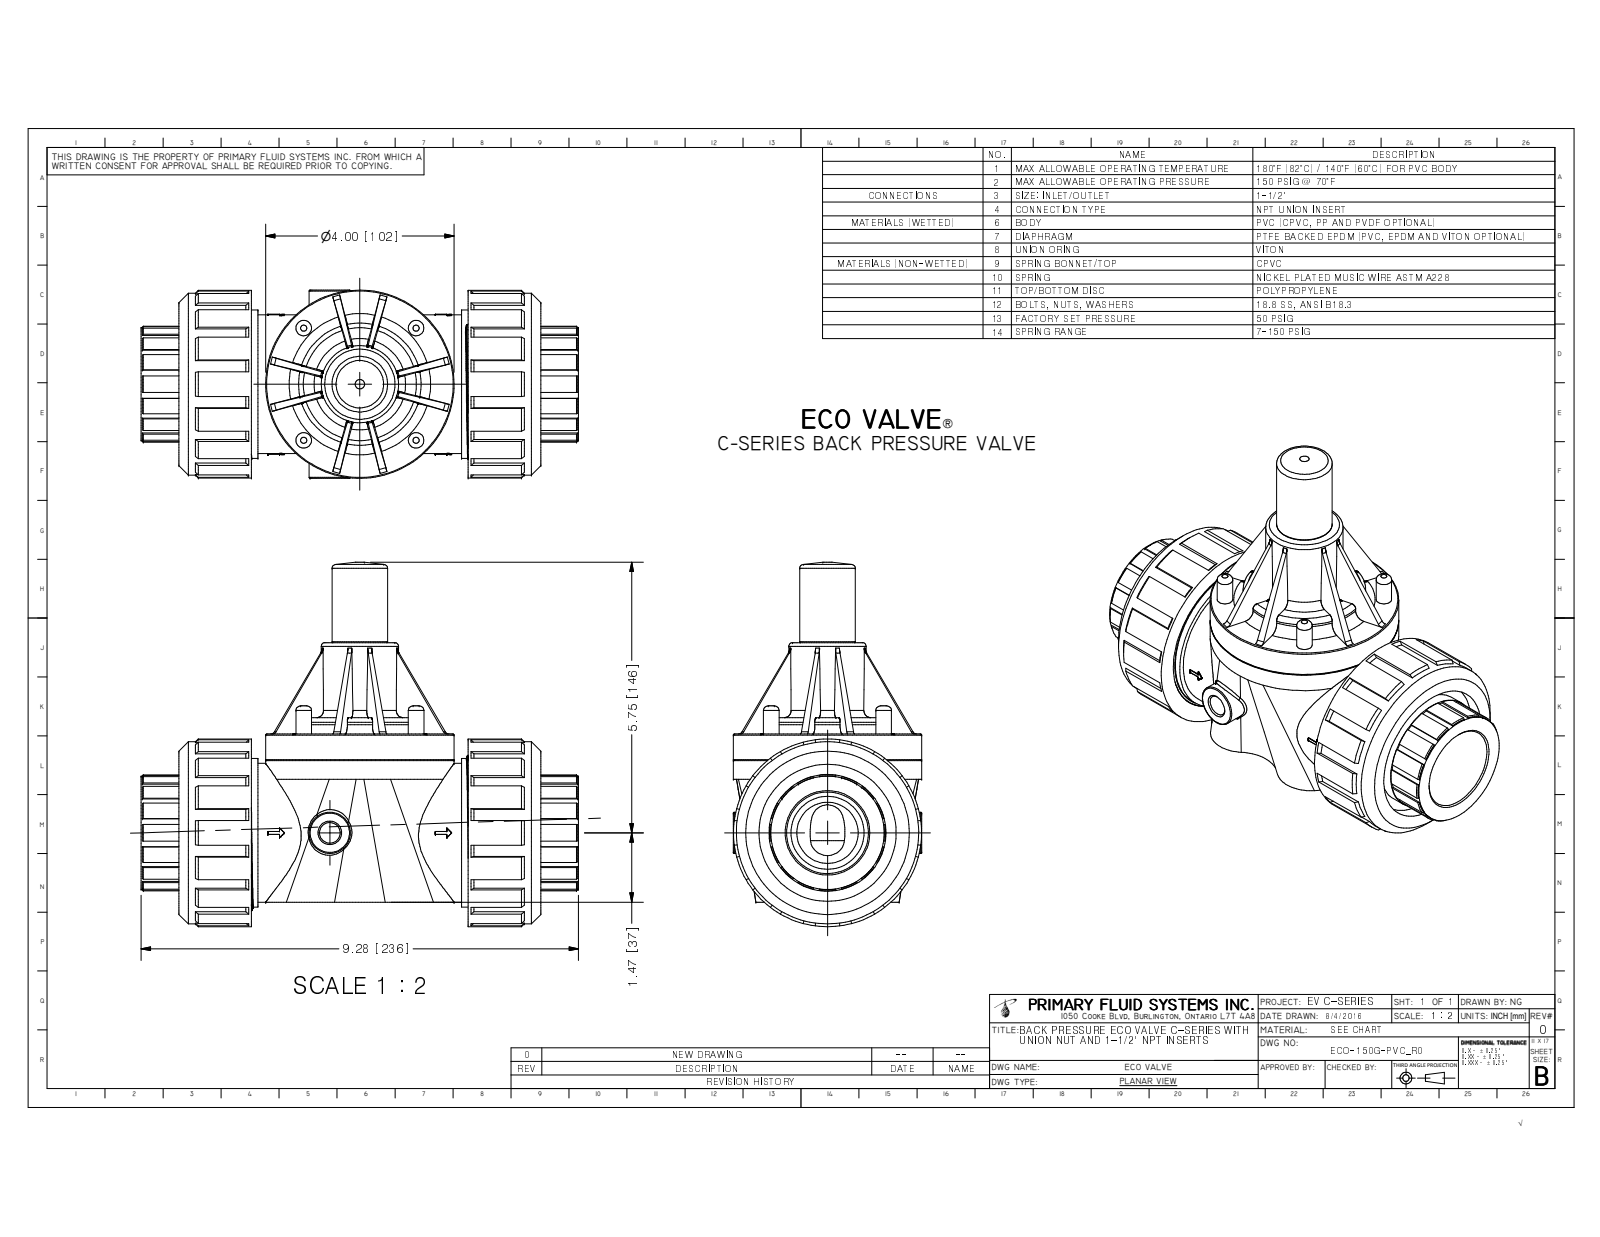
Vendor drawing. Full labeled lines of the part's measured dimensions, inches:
Part name (STEP PRODUCT): ECO-150G-PVC_R0
STEP written by: Autodesk Inventor 2009 (AUTOMOTIVE_DESIGN)
Units: inches
Bodies: 1 solid, 744 faces (344 planar, 135 cylindrical, 265 other)
Overall size (bounding box): 9.28 × 7.744 × 4
Volume: 89.4 in³ · Surface area: 266.5 in²
Round holes (diameter × count): ⌀0.23 ×4, ⌀0.437 ×1, ⌀1.734 ×1, ⌀2.91 ×1
Round bosses / shafts (diameter × count): ⌀0.4 ×4, ⌀0.33 ×4, ⌀4 ×1, ⌀3.99 ×1, ⌀3.87 ×1, ⌀3.158 ×1, ⌀2.947 ×1, ⌀2.919 ×1
Partial cylindrical surfaces — rounded edges, fillets, slot ends (radius × count): R0.1 ×15, R0.128 ×7, R0.05 ×4, R0.225 ×4, R0.412 ×1, R0.431 ×1, R0.471 ×1, R0.875 ×1
Main face-to-face distances: 1.032, 5.632, 0.508, 1.54, 6.14, 7.172, 0.3, 4.6, 6.872, 7.38
Hole centre spacings: 2.385, 3.373
